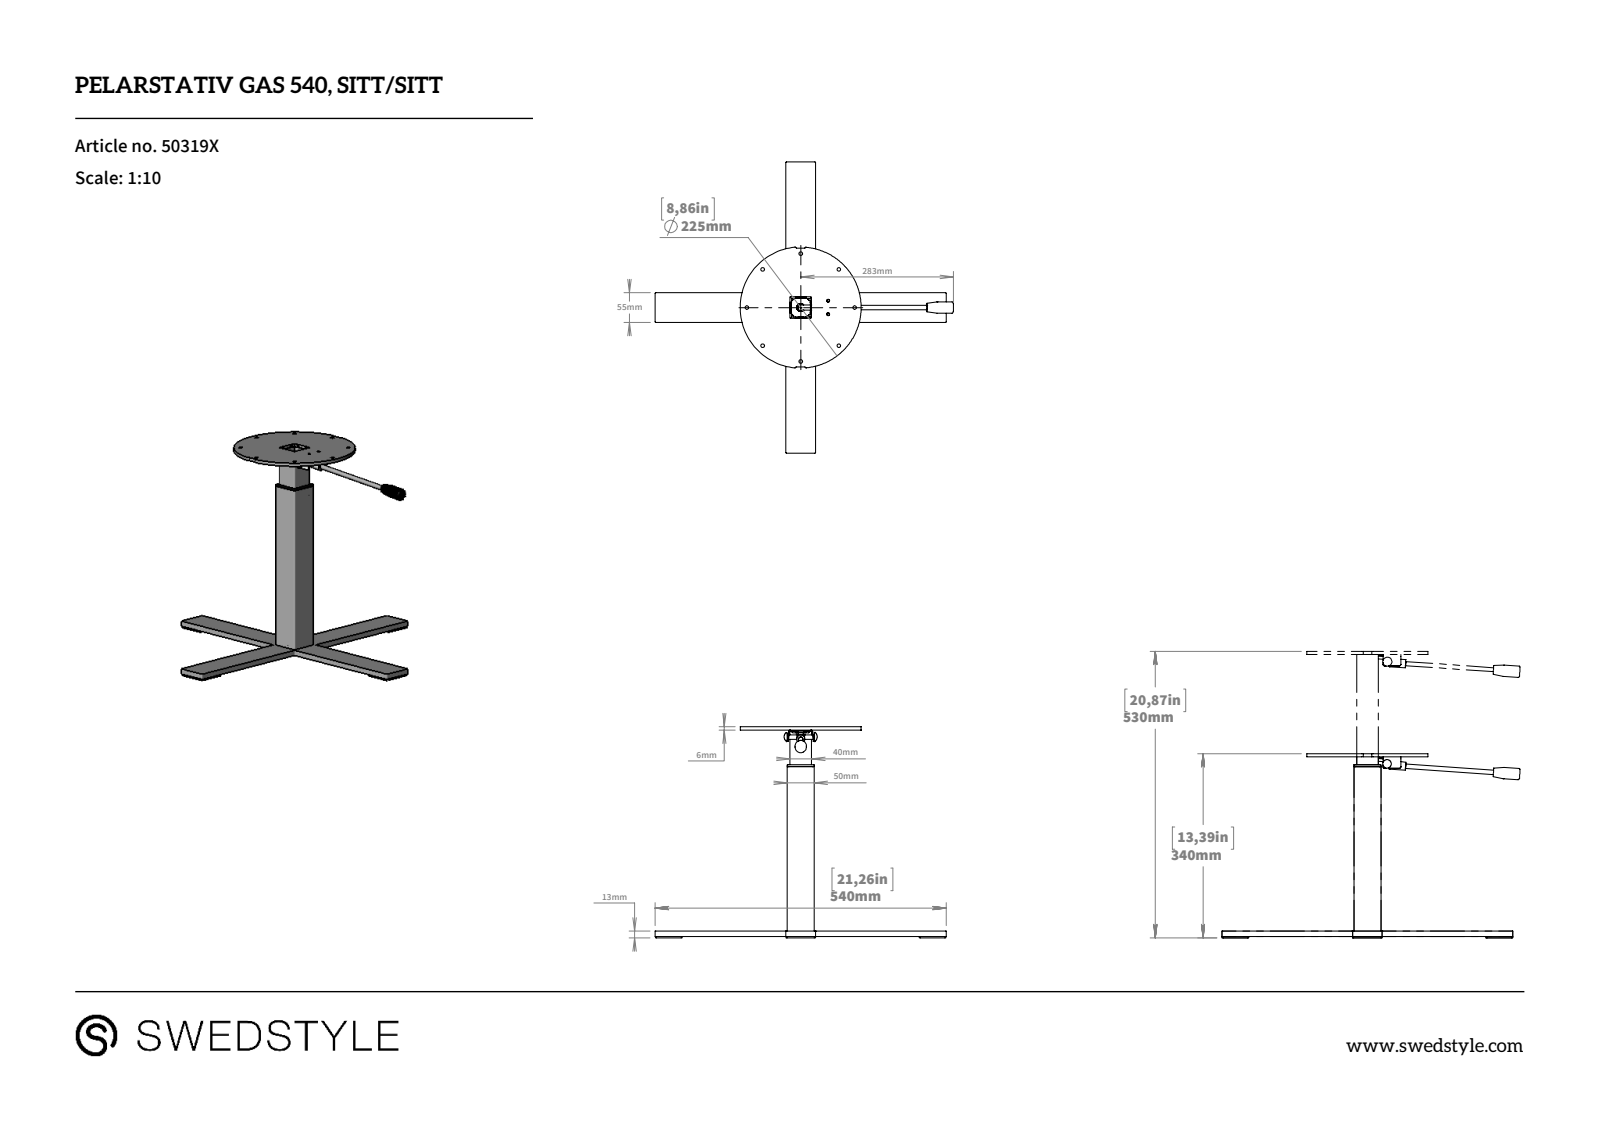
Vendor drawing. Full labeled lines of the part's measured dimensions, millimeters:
Part name (STEP PRODUCT): 50319X_Pelarstativ gas 540, spak, Sitt_Sitt
STEP written by: SolidWorks 2017 (CONFIG_CONTROL_DESIGN)
Units: millimetres
Bodies: 0 solids, 304 faces (135 planar, 113 cylindrical, 56 other)
Overall size (bounding box): 553.39 × 540 × 391.5
Round holes (diameter × count): ⌀6.6 ×12, ⌀3.4 ×4, ⌀5 ×2, ⌀6.7 ×1, ⌀9 ×1
Round bosses / shafts (diameter × count): ⌀8 ×2, ⌀225 ×1, ⌀21 ×1, ⌀15 ×1
Partial cylindrical surfaces — rounded edges, fillets, slot ends (radius × count): R2 ×30, R1 ×8, R2.5 ×8, R0.5 ×4, R2.75 ×4, R3 ×4, R4 ×2, R6 ×1
Main face-to-face distances: 10, 2, 5, 45, 43, 7, 38, 389, 379, 6
Hole centre spacings: 76.54, 84.72, 100, 102.85, 118.23, 141.42, 184.78, 24.04
